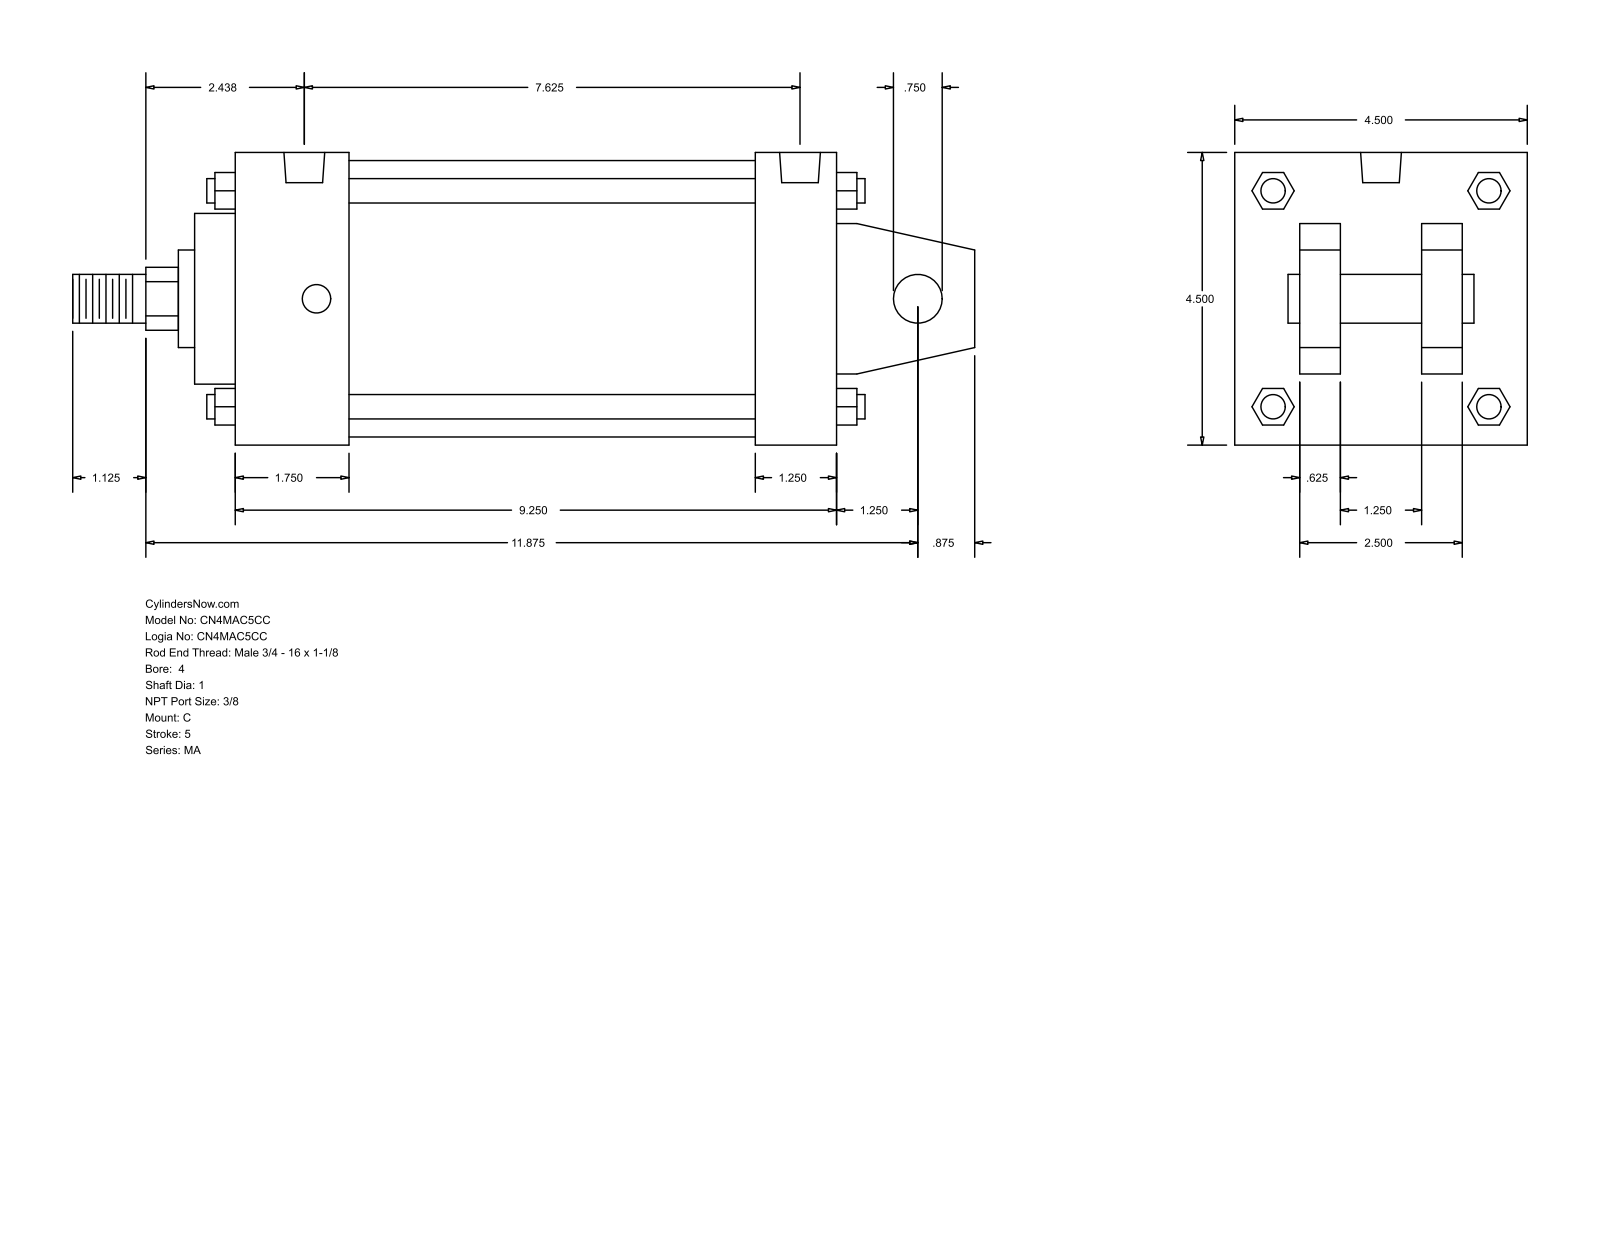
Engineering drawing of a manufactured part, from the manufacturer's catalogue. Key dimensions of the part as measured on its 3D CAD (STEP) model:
Part name (STEP PRODUCT): MA_C__0400_1
STEP written by: GSSL Pune (CONFIG_CONTROL_DESIGN)
Units: millimetres
Bodies: 0 solids, 141 faces (109 planar, 32 cylindrical, 0 other)
Overall size (bounding box): 352.43 × 114.3 × 114.3
Round holes (diameter × count): ⌀11.11 ×4, ⌀15.93 ×2
Round bosses / shafts (diameter × count): ⌀9.53 ×4, ⌀19.05 ×2, ⌀107.95 ×1, ⌀66.67 ×1, ⌀38.1 ×1, ⌀25.4 ×1
Partial cylindrical surfaces — rounded edges, fillets, slot ends (radius × count): R12.29 ×1
Main face-to-face distances: 114.3, 234.96, 15.87, 31.76, 73.03, 41.27, 25.4, 88.9, 47.63, 203.2
Hole centre spacings: 184.15, 4.76, 4.77, 188.91, 188.92, 193.68
